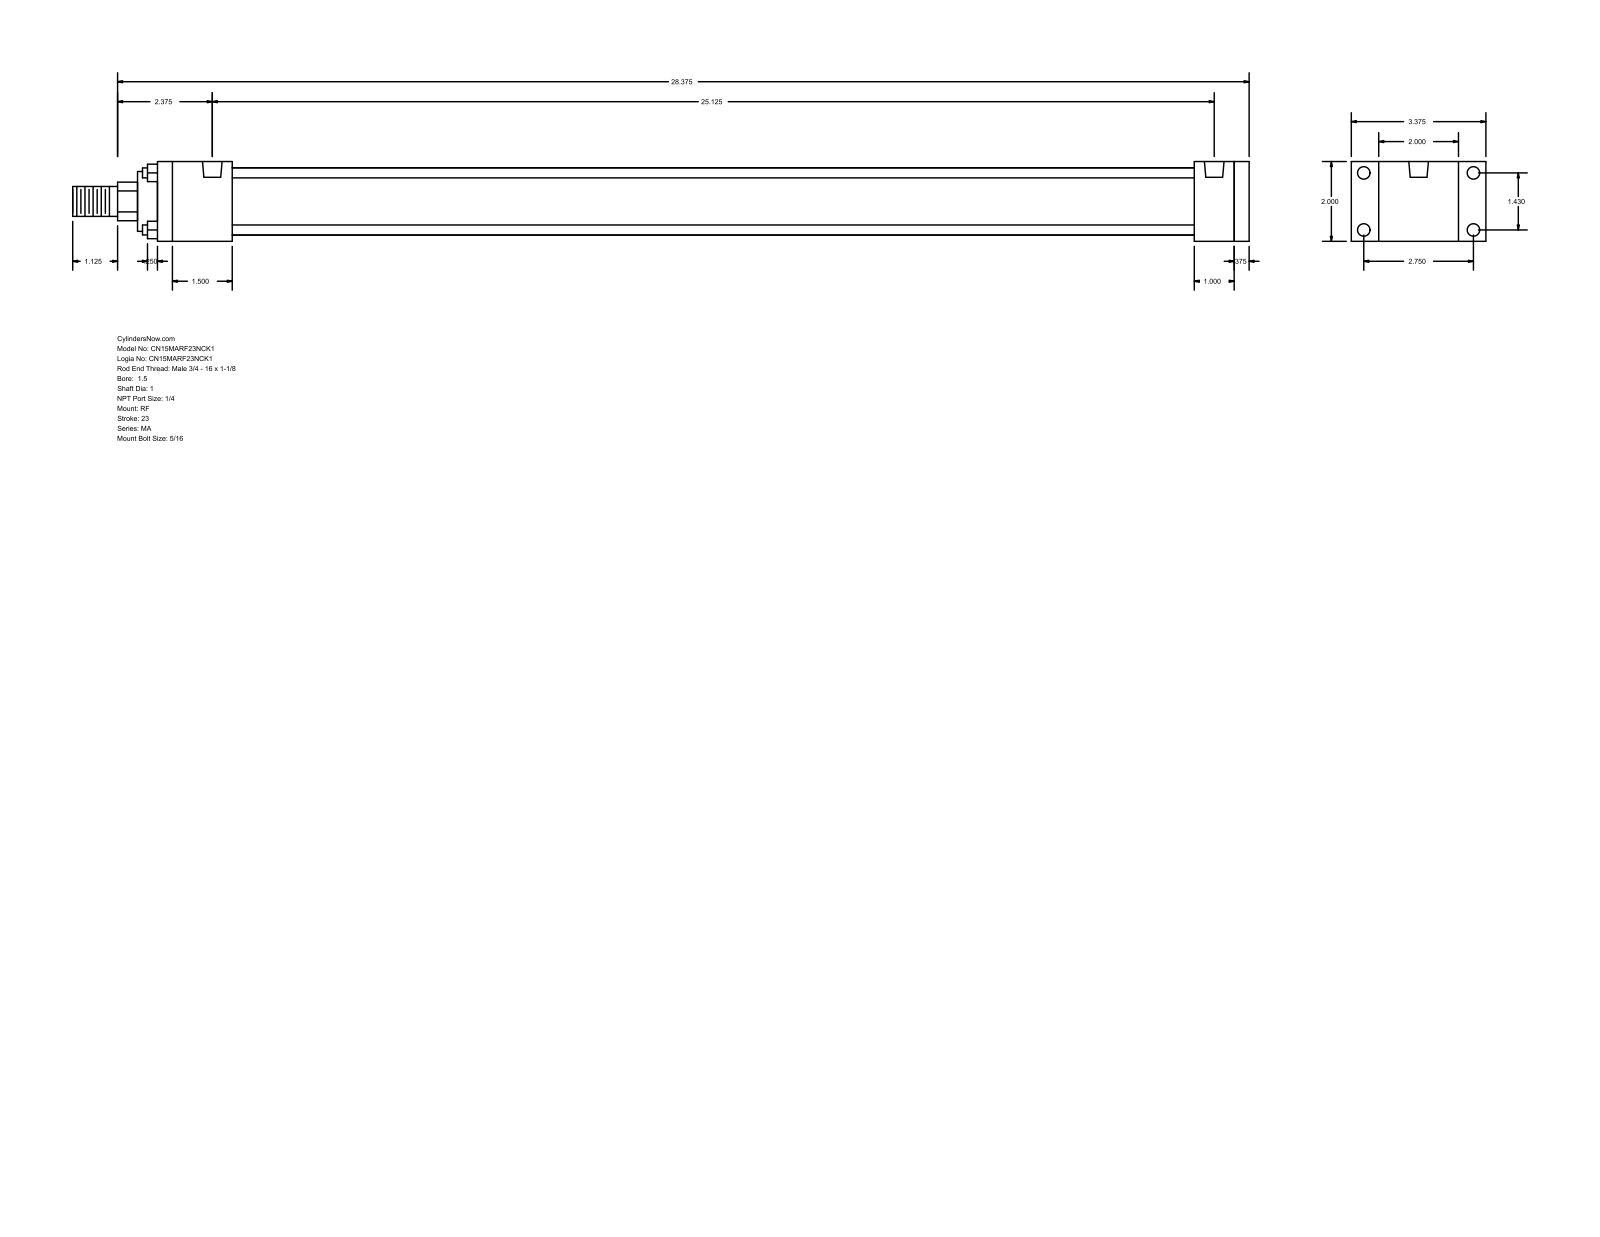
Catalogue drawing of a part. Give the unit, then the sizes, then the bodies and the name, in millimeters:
Units: millimetres
Overall size (bounding box): 749.3 × 85.72 × 50.8
Round holes (diameter × count): ⌀7.94 ×8, ⌀12.49 ×2
Round bosses / shafts (diameter × count): ⌀6.35 ×4, ⌀42.93 ×1, ⌀38.1 ×1, ⌀25.4 ×1, ⌀19.05 ×1
Partial cylindrical surfaces — rounded edges, fillets, slot ends (radius × count): R12.29 ×1
Main face-to-face distances: 50.8, 9.53, 685.8, 25.4, 695.33, 660.4, 34.93, 47.63, 612.77, 638.17
Hole centre spacings: 36.32, 69.84, 78.72, 638.17
Bodies: 0 solids, 92 faces (64 planar, 28 cylindrical, 0 other)
Part name (STEP PRODUCT): MA_RF__0150_1
STEP written by: GSSL Pune (CONFIG_CONTROL_DESIGN)
